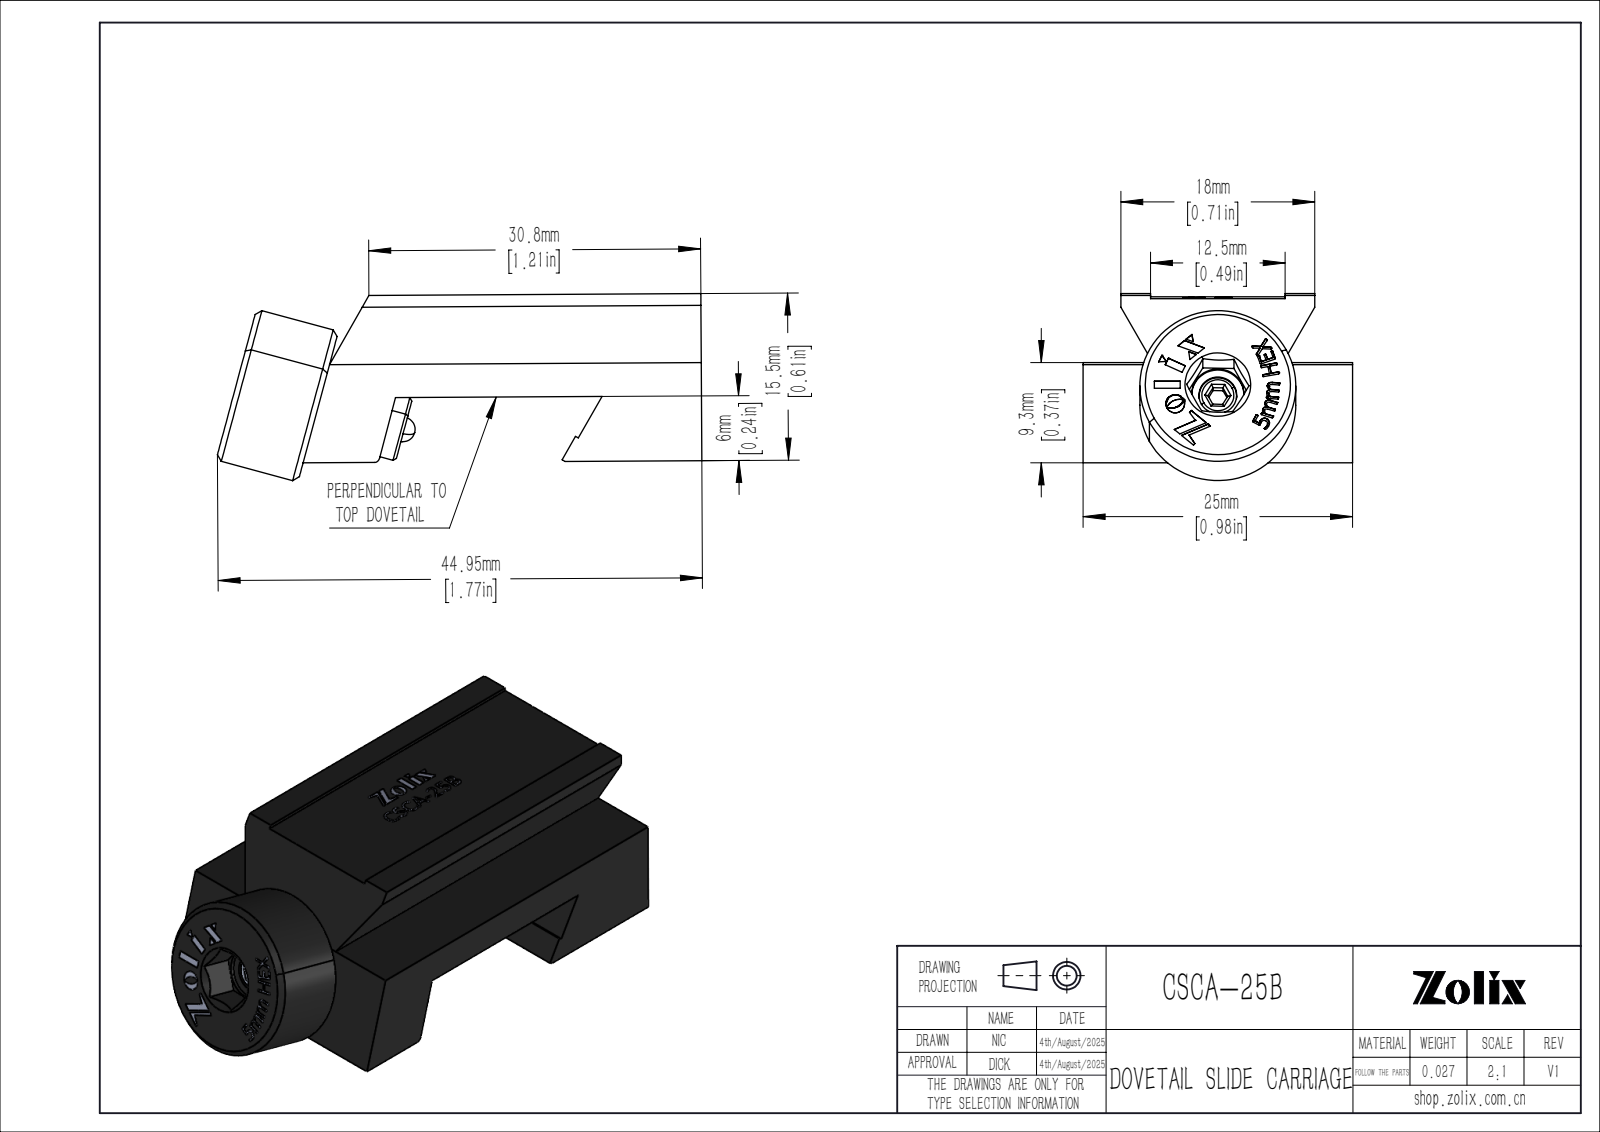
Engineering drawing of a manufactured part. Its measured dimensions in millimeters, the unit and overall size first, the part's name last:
Units: millimetres
Overall size (bounding box): 44.95 × 25 × 17.35
Round holes (diameter × count): ⌀2.15 ×1, ⌀2.54 ×1, ⌀3.18 ×1, ⌀3.51 ×1, ⌀4.85 ×1, ⌀5 ×1, ⌀10.29 ×1
Round bosses / shafts (diameter × count): ⌀14.48 ×1, ⌀10.03 ×1, ⌀6 ×1, ⌀3.48 ×1, ⌀3 ×1, ⌀2.29 ×1
Partial cylindrical surfaces — rounded edges, fillets, slot ends (radius × count): R0.5 ×1
Main face-to-face distances: 3.09, 6.12, 9.21, 15.22, 9.1, 6.01, 25, 15.2, 6.42, 9.51
Volume: 9 774 mm³ · Surface area: 5 185 mm²
Bodies: 5 solids, 705 faces (494 planar, 45 cylindrical, 166 other)
Part name (STEP PRODUCT): CSCA-25B
STEP written by: SolidWorks 2020 (CONFIG_CONTROL_DESIGN)
